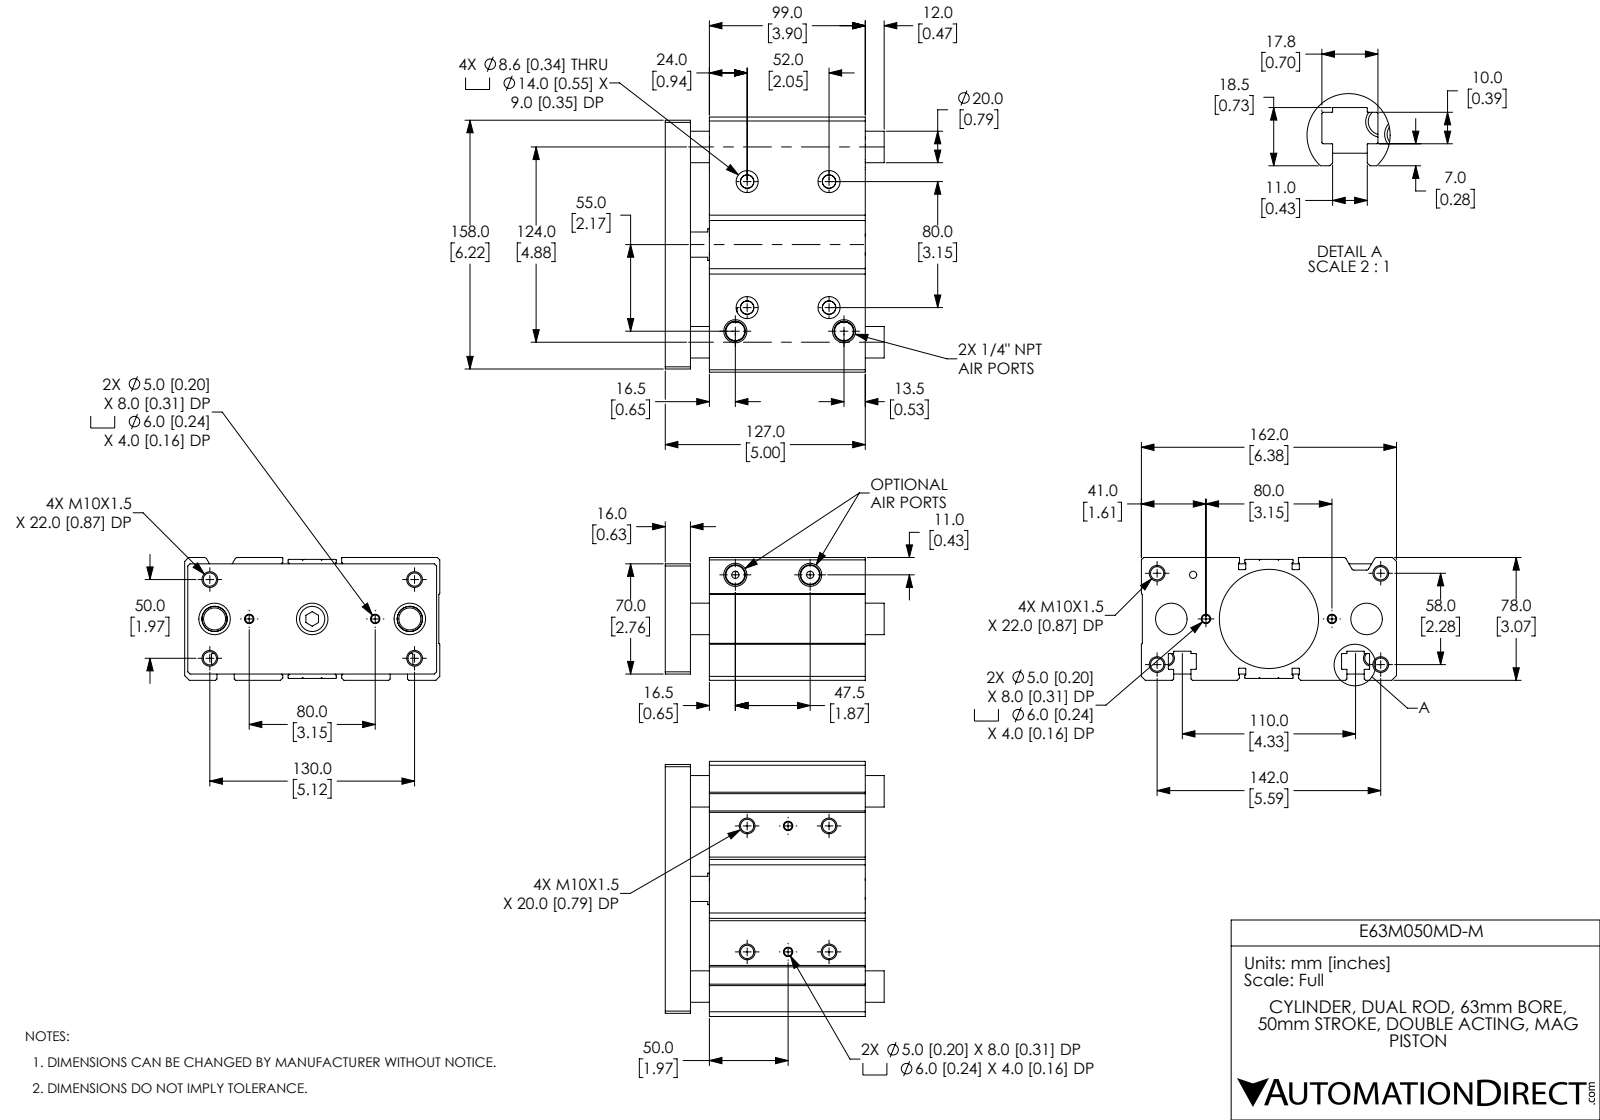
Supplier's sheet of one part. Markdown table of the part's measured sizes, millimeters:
| quantity | value |
| --- | --- |
| part name | E63M050MD-M; E63M050MD-M_BODY; E63M050MD-M_ENDPLATE |
| STEP written by | SolidWorks 2019 (CONFIG_CONTROL_DESIGN) |
| units | millimeters |
| bodies | 5 solids, 421 faces (139 planar, 190 cylindrical, 92 other) |
| overall size | 162 × 139 × 78 |
| volume | 1 171 000 mm³ |
| surface area | 205 593 mm² |
| round holes (diameter × count) | 8.38 × 12, 5 × 4, 6 × 4, 8.6 × 4, 14 × 4, 4.57 × 3, 10 × 3, 20 × 3, 16 × 2, 20 × 1, 63 × 1, 63 × 1 |
| round bosses / shafts (diameter × count) | 16 × 1 |
| partial cylindrical surfaces (radius × count) | 0.2 × 32, 0.4 × 28, 1.5 × 4, 0.3 × 2 |
| main face-to-face distances | 12, 28, 16, 78, 99, 111, 127, 4, 120.25, 104.25 |
| hole center spacings | 7.21, 25.18, 26, 30.36, 35.36, 42.45, 54.33, 69.64 |
